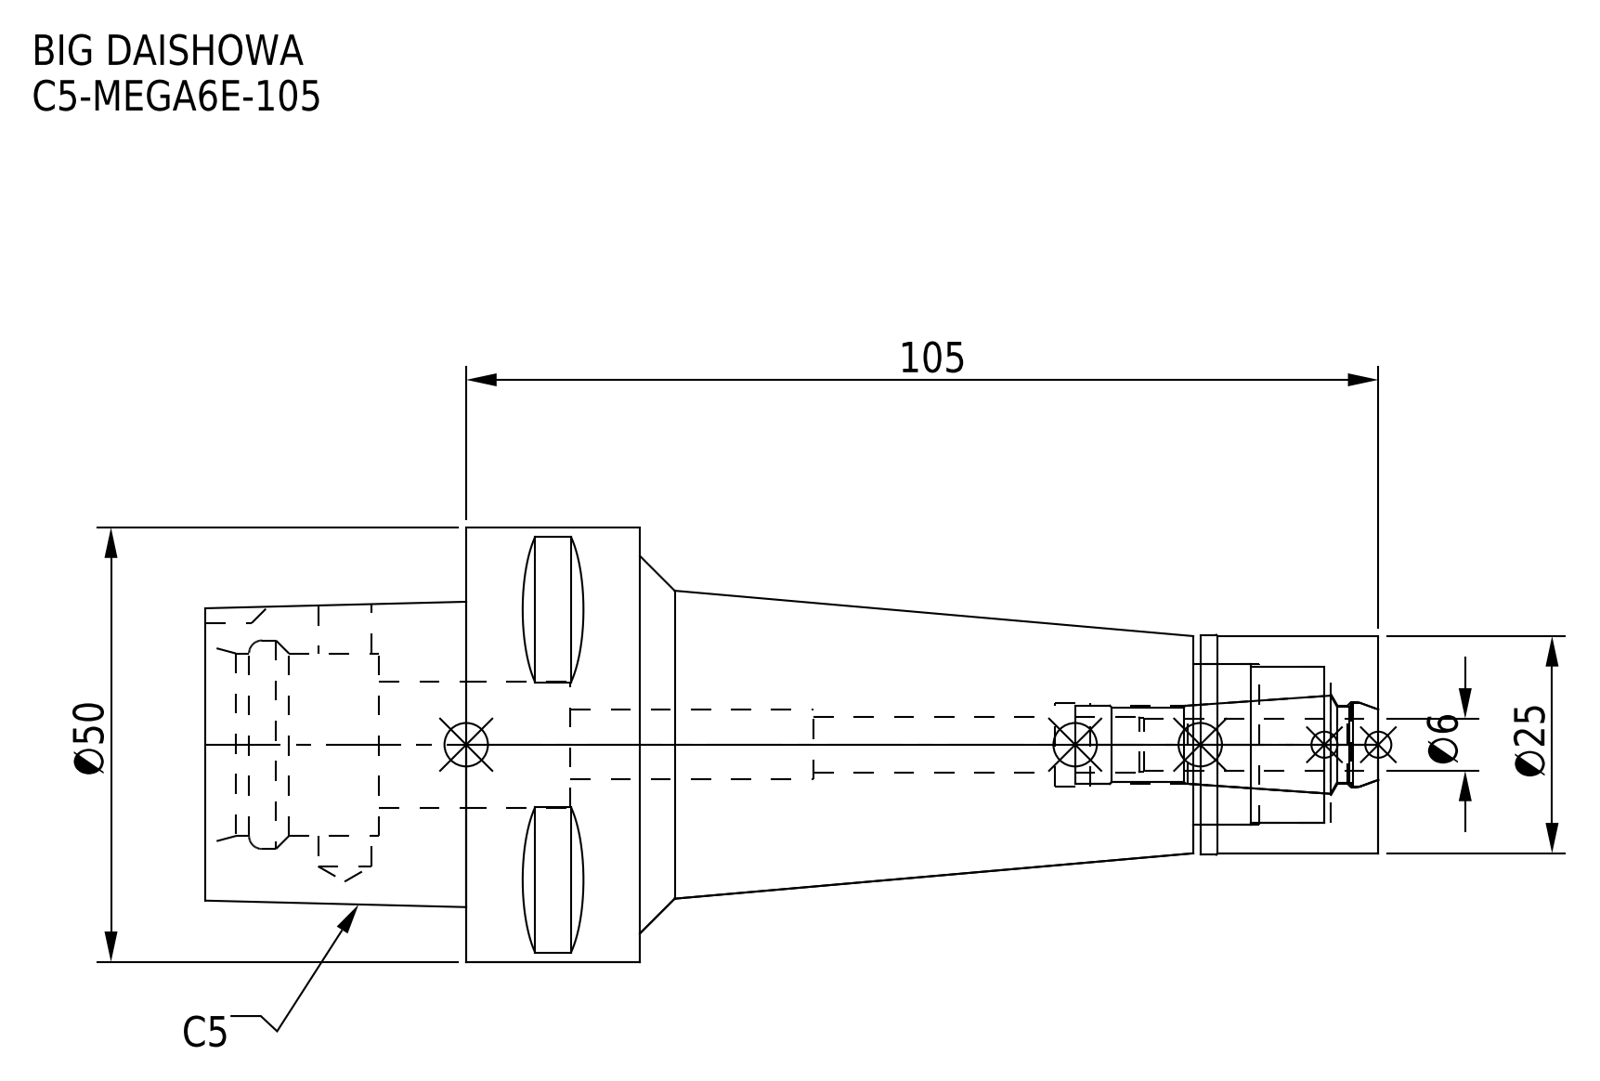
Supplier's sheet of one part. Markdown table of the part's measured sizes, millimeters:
| quantity | value |
| --- | --- |
| part name | C5-MEGA6E-105; C5-MEGA6E-105-060.stp; MEN6_1.stp; C5-MEGA6E-105_1.stp (+3 more) |
| STEP written by | SolidWorks 2019 (CONFIG_CONTROL_DESIGN) |
| units | millimeters |
| bodies | 2 solids, 100 faces (37 planar, 39 cylindrical, 24 other) |
| overall size | 135 × 50 × 50 |
| volume | 107 810 mm³ |
| surface area | 24 862 mm² |
| round holes (diameter × count) | 6.1 × 1, 6.4 × 1, 8 × 1, 9 × 1, 9.6 × 1, 9.9 × 1, 14.5 × 1, 18 × 1, 18.5 × 1, 21 × 1, 24 × 1 |
| round bosses / shafts (diameter × count) | 50 × 1, 25.3 × 1, 25 × 1 |
| partial cylindrical surfaces (radius × count) | 4 × 1 |
| main face-to-face distances | 20, 30, 85, 105, 50, 135, 20.5, 64.5, 84.5, 114.5 |
